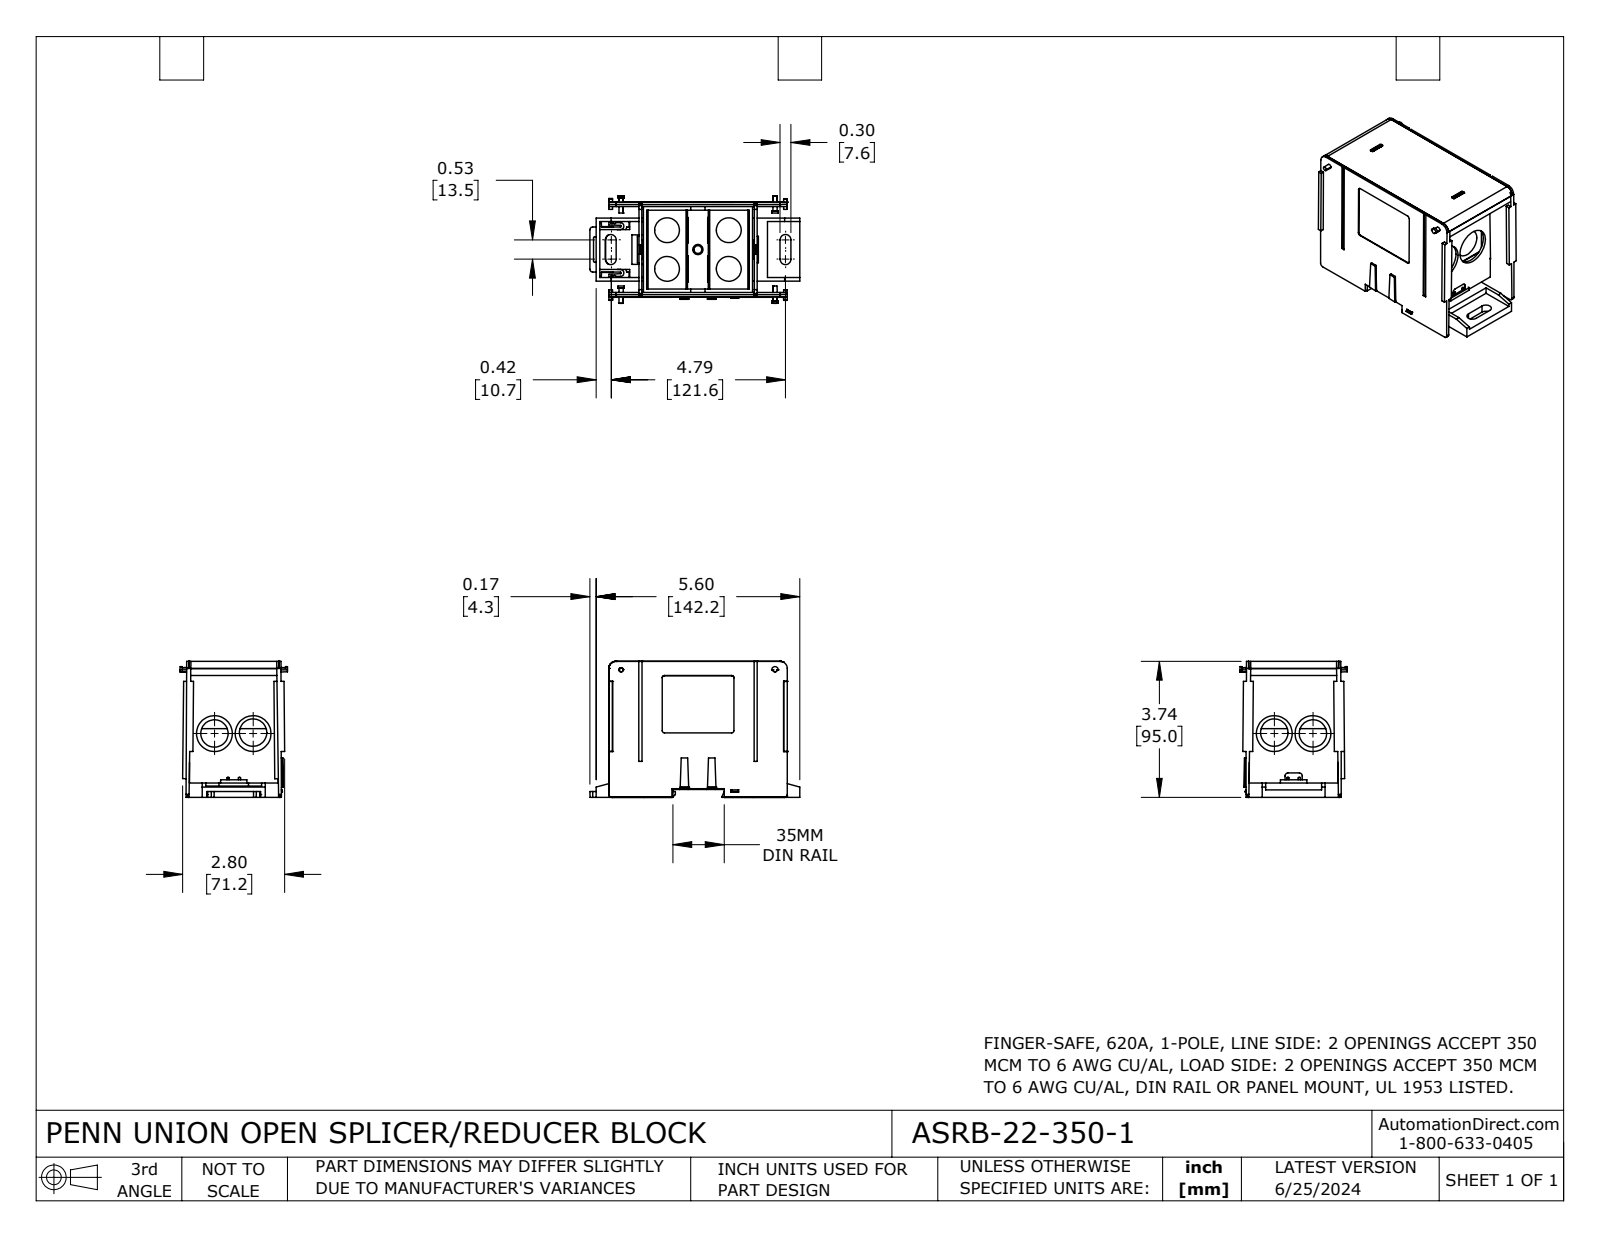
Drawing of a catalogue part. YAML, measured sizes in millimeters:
part_name: "ASRB-22-350-1"
step_written_by: "SolidWorks 2023 (CONFIG_CONTROL_DESIGN)"
units: millimeters
bodies: {solids: 10, faces: 779, planar: 551, cylindrical: 157, other: 71}
overall_size: [146.6, 95, 75.1]
volume: 312000
surface_area: 150300
round_holes:
  - {diameter: 17.3, count: 4}
  - {diameter: 19.1, count: 2}
  - {diameter: 25, count: 2}
  - {diameter: 5.4, count: 1}
  - {diameter: 7.1, count: 1}
partial_cylinders:
  - {radius: 1, count: 26}
  - {radius: 1.5, count: 18}
  - {radius: 0.5, count: 16}
  - {radius: 2, count: 10}
  - {radius: 5, count: 10}
  - {radius: 0.3, count: 6}
  - {radius: 2.3, count: 4}
  - {radius: 3.8, count: 4}
face_to_face_distances: [2, 80.5, 64.5, 1.8, 62.7, 0.5, 5.5, 78.5, 82.5, 30.5]
hole_center_spacings: [27, 25.4, 43.1, 50.9, 0.7]
